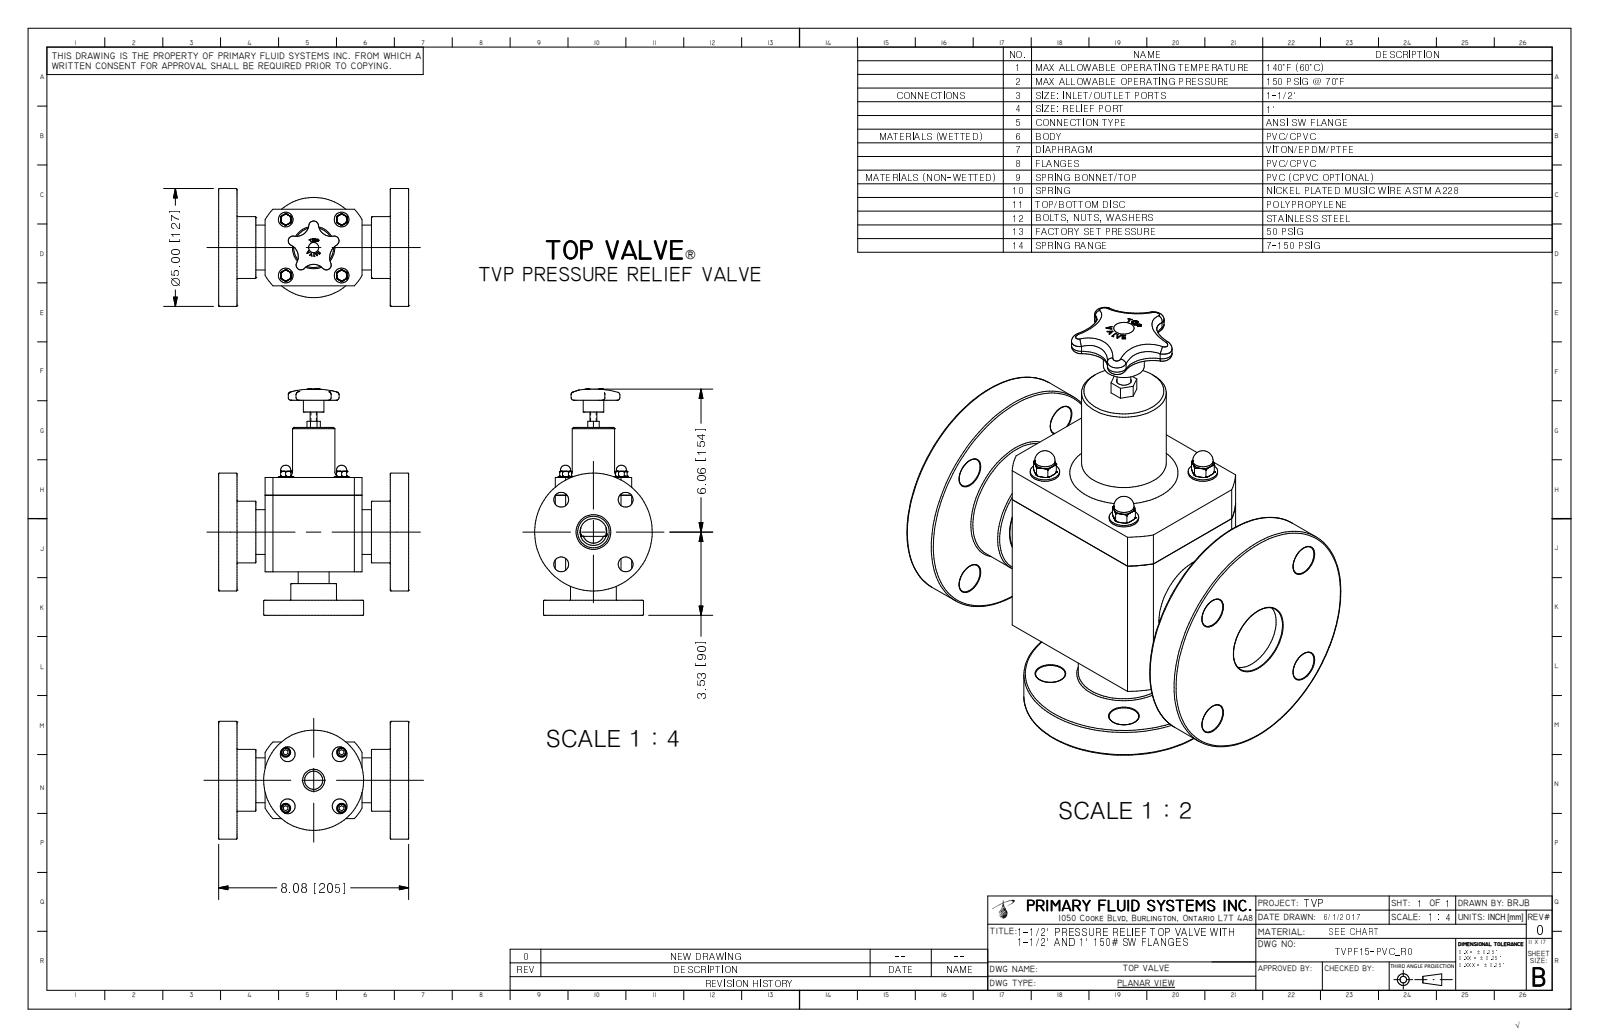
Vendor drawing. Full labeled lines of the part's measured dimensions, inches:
Part name (STEP PRODUCT): TVPF15-PVC_R0
STEP written by: Autodesk Inventor 2009 (AUTOMOTIVE_DESIGN)
Units: inches
Bodies: 1 solid, 424 faces (157 planar, 70 cylindrical, 197 other)
Overall size (bounding box): 9.593 × 8.08 × 5
Volume: 97.74 in³ · Surface area: 342.3 in²
Round holes (diameter × count): ⌀0.63 ×8, ⌀0.175 ×4, ⌀0.936 ×1, ⌀0.957 ×1, ⌀1.476 ×1, ⌀1.5 ×1
Round bosses / shafts (diameter × count): ⌀0.625 ×4, ⌀0.433 ×4, ⌀0.375 ×4, ⌀5 ×1, ⌀4.25 ×1, ⌀2.62 ×1, ⌀1.941 ×1, ⌀1.9 ×1
Partial cylindrical surfaces — rounded edges, fillets, slot ends (radius × count): R0.085 ×5, R0.205 ×5, R0.536 ×4, R0.656 ×4, R0.625 ×1, R0.745 ×1, R2.375 ×1
Main face-to-face distances: 0.78, 7.3, 8.08, 3.25, 1.978, 6.103, 1.197, 5.322, 6.52, 1.843
Hole centre spacings: 1.562, 1.937, 2.209, 2.294, 2.74, 0.117, 0.117, 1.679
